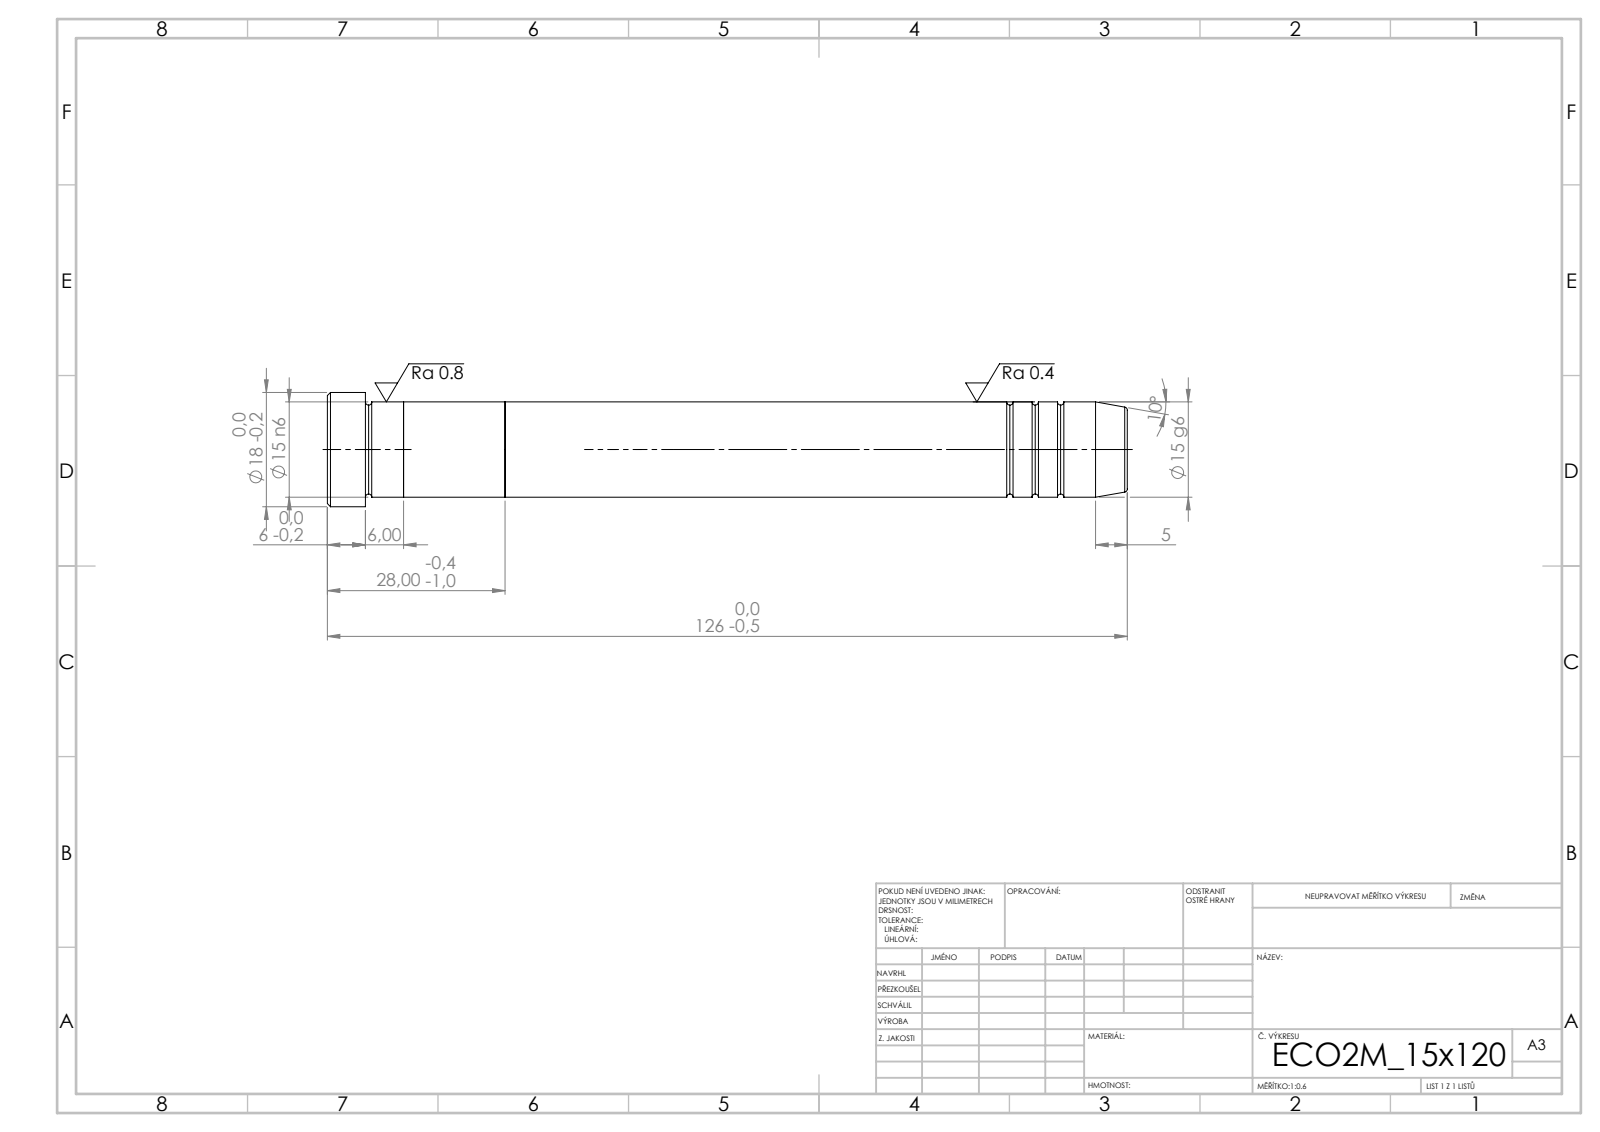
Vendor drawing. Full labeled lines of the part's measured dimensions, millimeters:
STEP written by: SolidWorks 2019 (CONFIG_CONTROL_DESIGN)
Units: millimetres
Bodies: 3 solids, 43 faces (7 planar, 14 cylindrical, 22 other)
Overall size (bounding box): 126 × 18 × 18
Volume: 22 552 mm³ · Surface area: 7 233 mm²
Round bosses / shafts (diameter × count): ⌀18 ×1, ⌀15 ×1
Main face-to-face distances: 16, 28, 12, 6, 98, 114, 126, 120, 22
